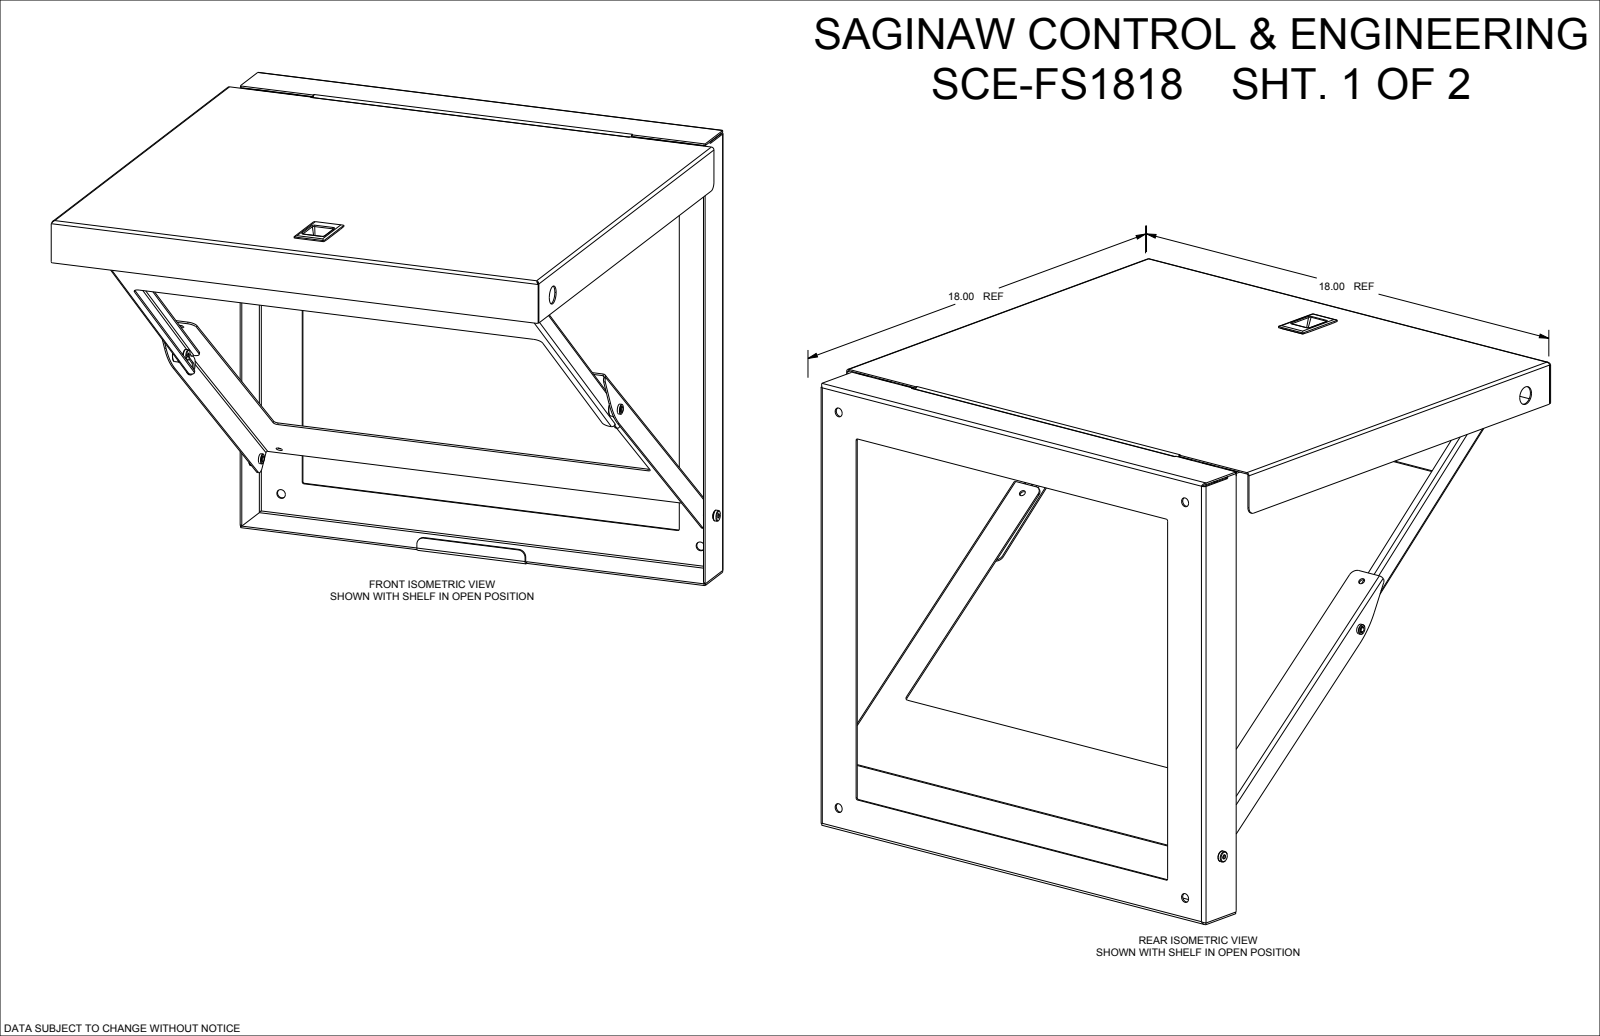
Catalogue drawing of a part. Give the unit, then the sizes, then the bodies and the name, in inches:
Units: inches
Overall size (bounding box): 18 × 18 × 15.99
Round holes (diameter × count): ⌀0.19 ×15, ⌀0.193 ×12, ⌀0.203 ×8, ⌀0.218 ×6, ⌀0.22 ×4, ⌀0.313 ×4, ⌀0.25 ×3, ⌀0.187 ×2, ⌀0.265 ×2, ⌀0.125 ×1, ⌀0.257 ×1, ⌀0.265 ×1
Round bosses / shafts (diameter × count): ⌀0.188 ×15, ⌀0.256 ×12, ⌀0.55 ×3, ⌀0.371 ×3, ⌀0.34 ×3, ⌀0.249 ×3, ⌀0.246 ×3, ⌀0.245 ×1
Partial cylindrical surfaces — rounded edges, fillets, slot ends (radius × count): R0.25 ×19, R0.014 ×16, R0.125 ×11, R0.06 ×8, R0.03 ×7, R0.031 ×7, R0.047 ×6, R0.095 ×6
Main face-to-face distances: 0.048, 0.06, 0.06, 0.048, 17.952, 15.85, 17.13, 18, 15.846, 15.894
Hole centre spacings: 1.5, 0.052, 0.874, 0.926, 1.736, 14.438, 14.464, 15.962
Volume: 41.4 in³ · Surface area: 1 542 in²
Bodies: 55 solids, 2030 faces (1102 planar, 442 cylindrical, 486 other)
Part name (STEP PRODUCT): SCE-FS1818
STEP written by: SolidWorks 2022 (AUTOMOTIVE_DESIGN)
